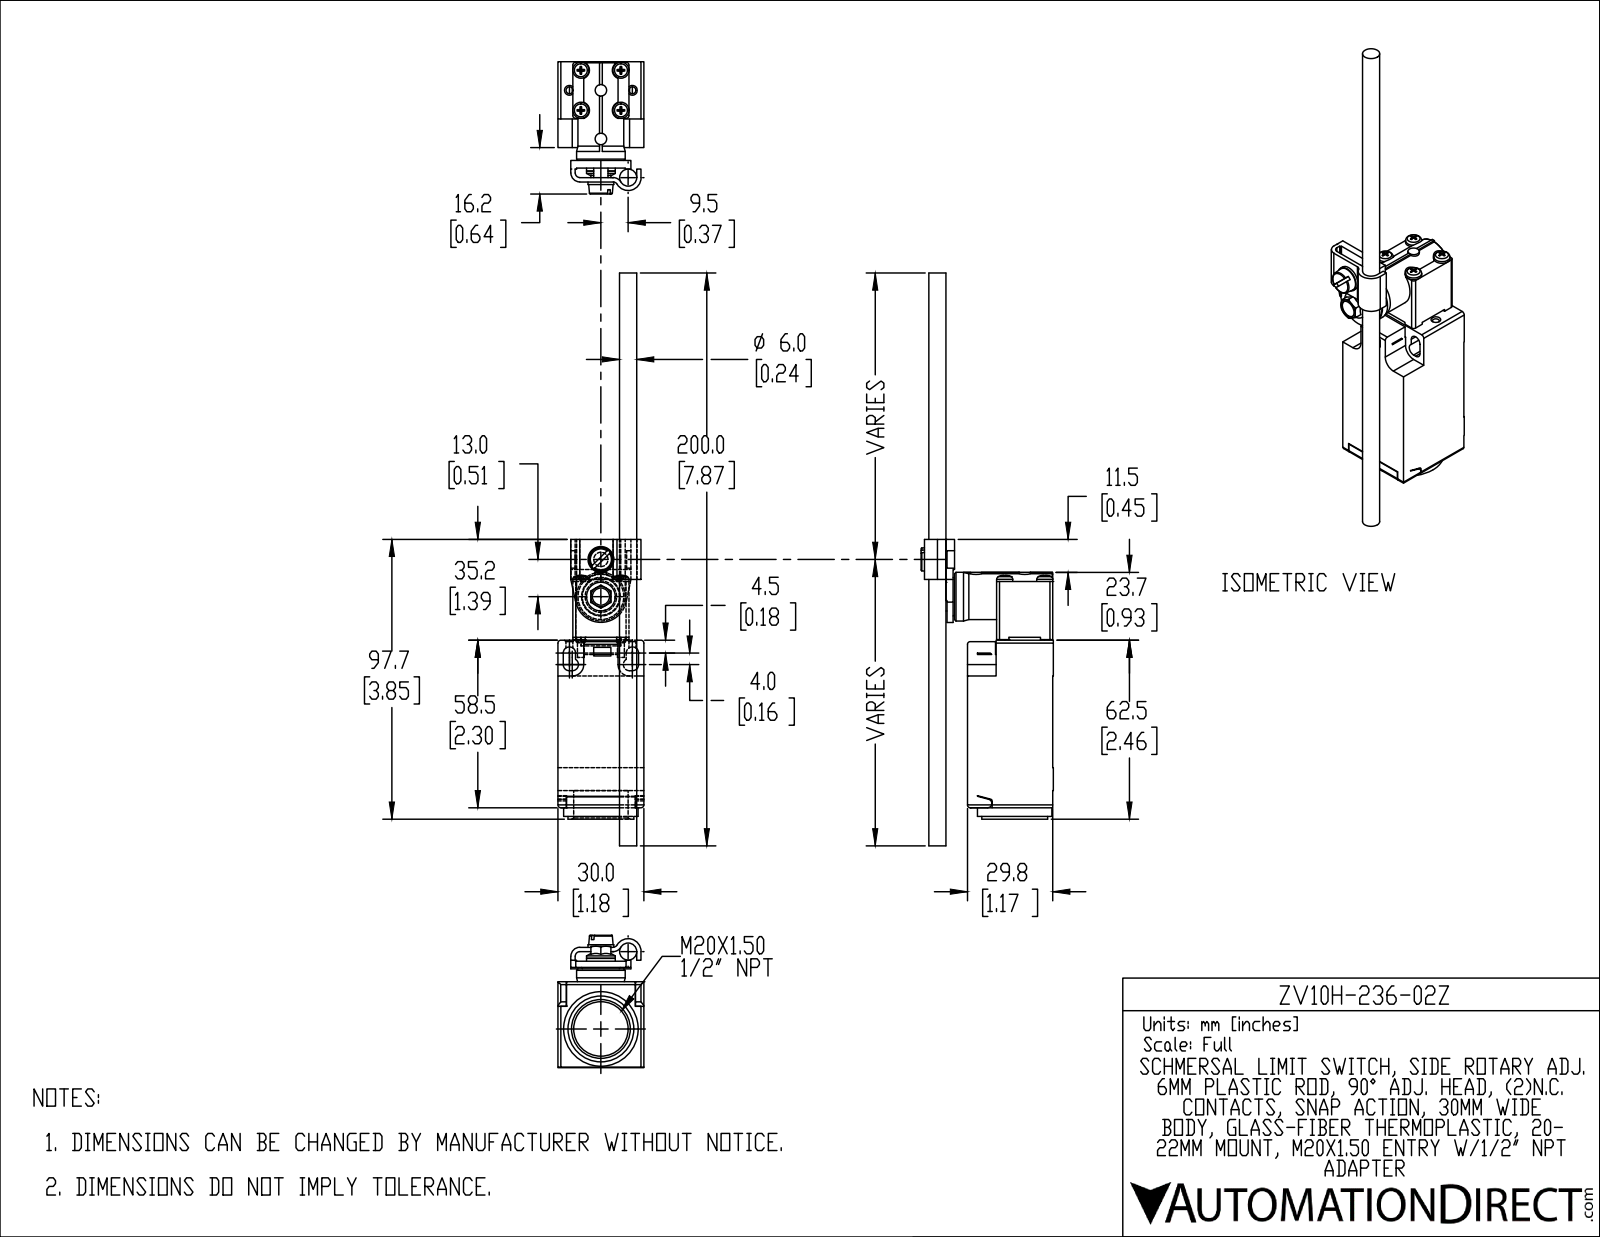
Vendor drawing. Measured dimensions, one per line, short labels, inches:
name: ZV10H-236-02Z
written by: SolidWorks 2019 (CONFIG_CONTROL_DESIGN)
unit: in
bodies: 2 solids, 444 faces (268 planar, 123 cylindrical, 53 other)
size: 7.874 × 1.819 × 1.181
volume: 4.096 in³; area: 32.5 in²
holes: 6× ⌀0.094, 4× ⌀0.126, 1× ⌀0.236, 1× ⌀0.512, 1× ⌀0.545, 1× ⌀0.748
bosses: 4× ⌀0.221, 4× ⌀0.213, 2× ⌀0.157, 1× ⌀1.024, 1× ⌀0.906, 1× ⌀0.669, 1× ⌀0.63, 1× ⌀0.543
rounds: 10× R0.039, 6× R0.085, 5× R0.059, 4× R0.118, 2× R0.063, 2× R0.122, 2× R0.157, 1× R0.008
face distances: 1.181, 1.173, 0.205, 0.976, 0.177, 0.281, 0.772, 0.236, 0.118, 1.455
hole spacings: 0.317, 0.39, 0.551, 0.76, 0.308, 0.433, 0.454, 0.497
